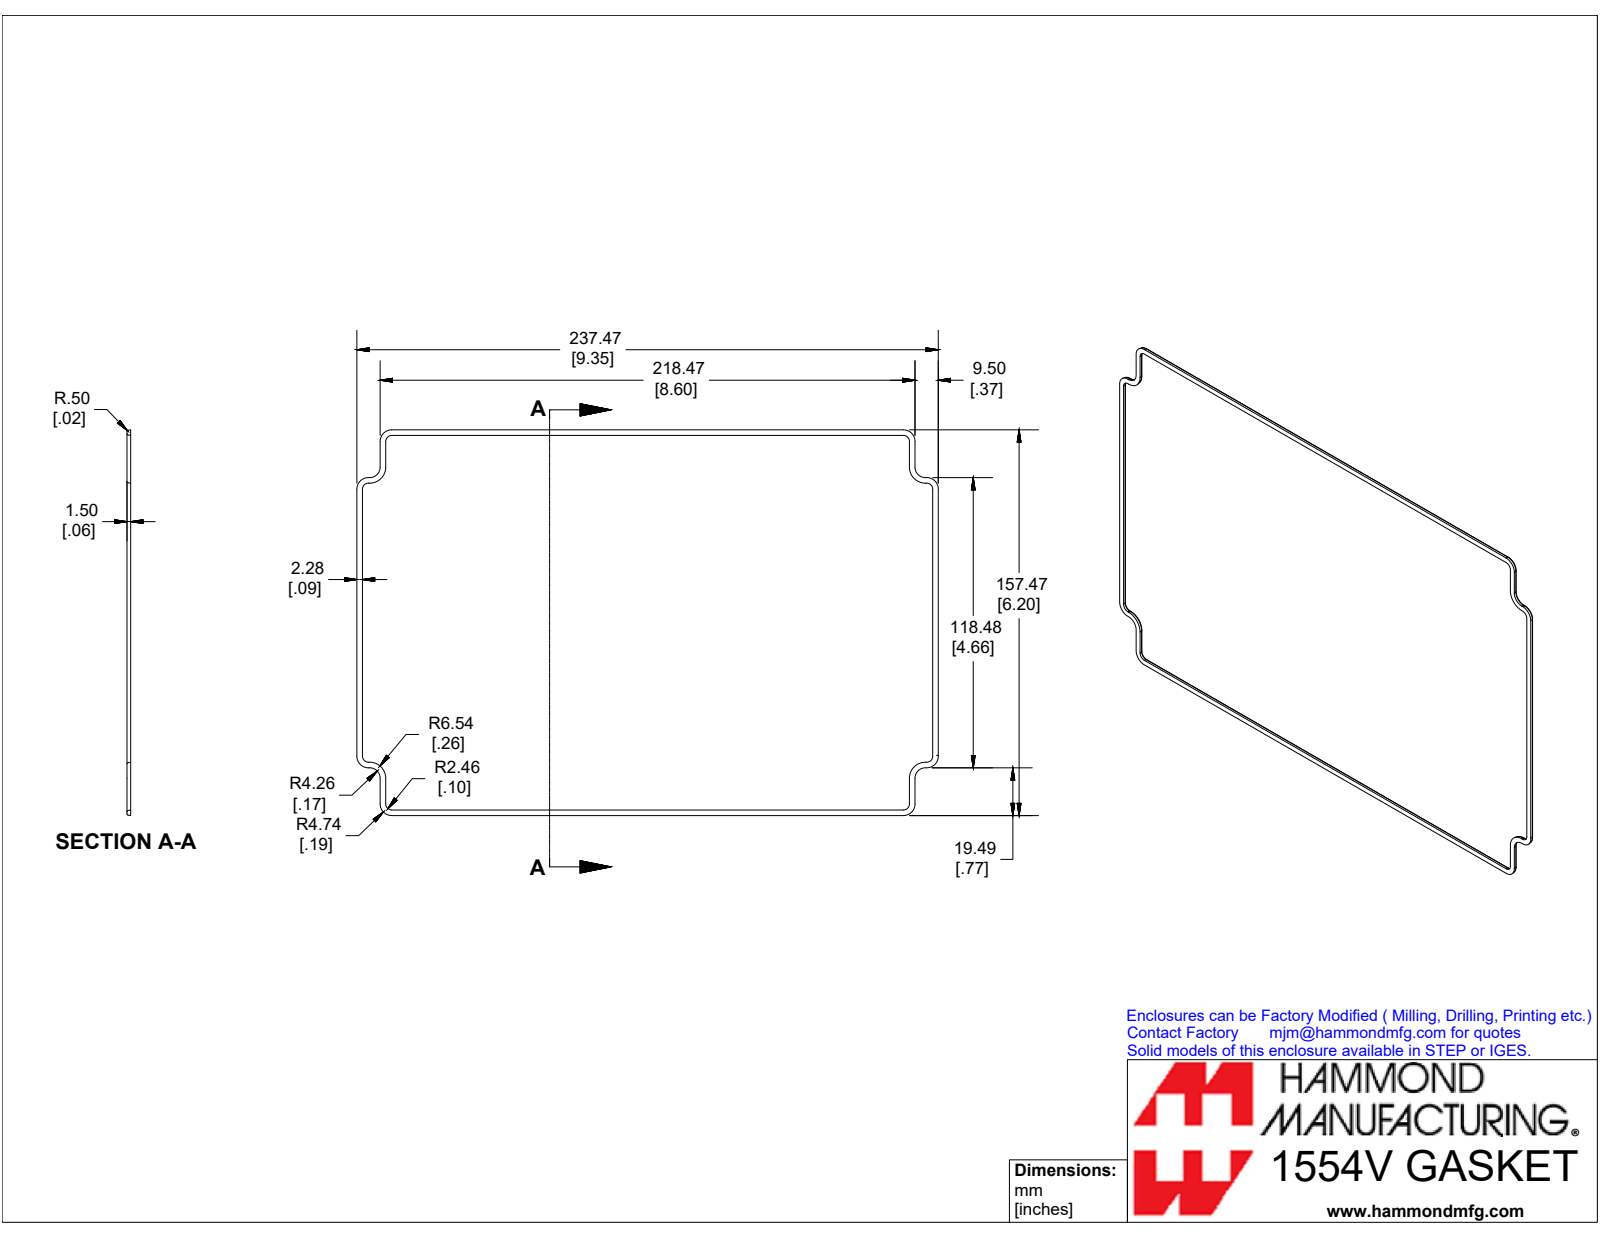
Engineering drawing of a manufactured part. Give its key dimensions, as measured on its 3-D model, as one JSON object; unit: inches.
{"part_name": "1554VGASKET", "step_written_by": "SolidWorks 2019 (CONFIG_CONTROL_DESIGN)", "units": "inches", "bodies": {"solids": 1, "faces": 96, "planar": 25, "cylindrical": 23, "other": 48}, "overall_size": [9.351, 6.201, 0.063], "volume_in3": 0.147, "surface_area_in2": 8.267, "partial_cylinders_radius": [[0.02, 16]], "face_to_face_distances": [0.063, 9.121, 6.018, 6.019, 0.369, 8.752, 8.384, 5.262, 0.756, 0.756]}
